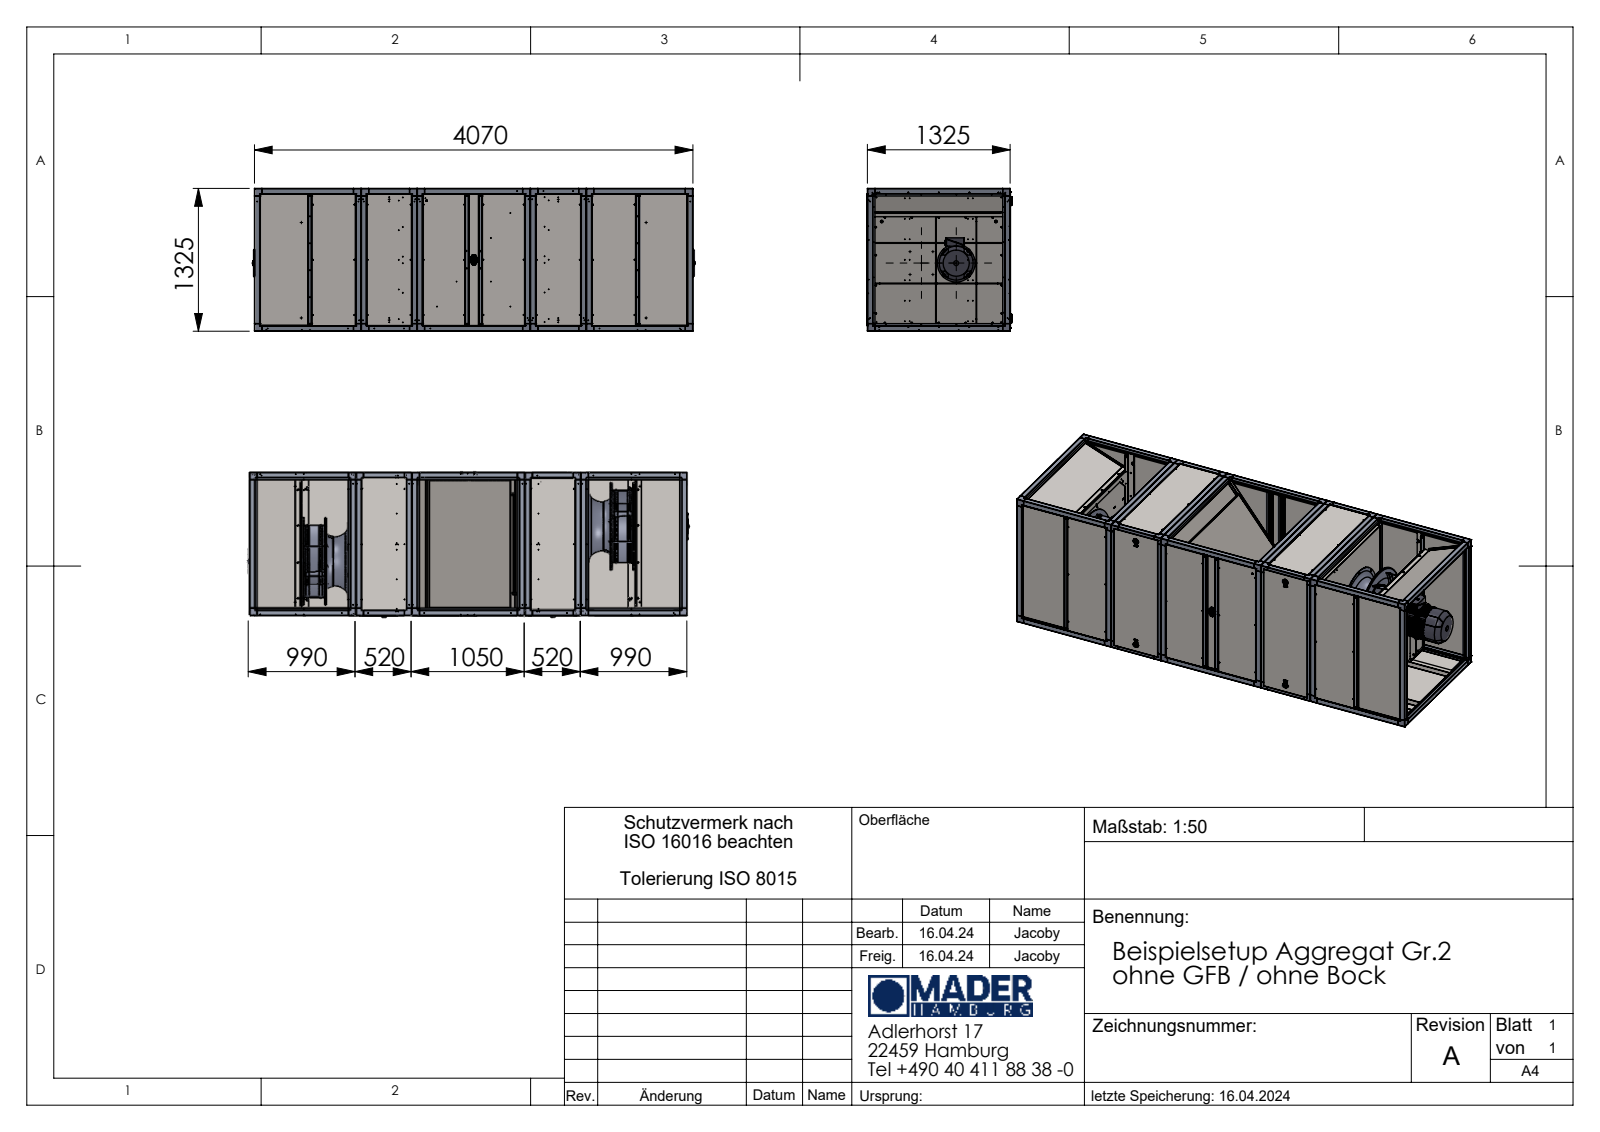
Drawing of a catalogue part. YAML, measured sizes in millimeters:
part_name: "Beispielsetup Aggregat Groesse 2 ohne GFB_ohne Bock"
step_written_by: "SolidWorks 2019 (CONFIG_CONTROL_DESIGN)"
units: millimeters
bodies: {solids: 341, faces: 24624, planar: 13058, cylindrical: 8482, other: 3084}
overall_size: [4108, 1344.73, 1325]
volume: 184600000
surface_area: 133200000
round_holes:
  - {diameter: 5, count: 200}
  - {diameter: 7, count: 82}
  - {diameter: 10, count: 65}
  - {diameter: 5.5, count: 34}
  - {diameter: 9, count: 34}
  - {diameter: 6, count: 33}
  - {diameter: 6.5, count: 32}
  - {diameter: 5.2, count: 28}
  - {diameter: 6.8, count: 19}
  - {diameter: 15, count: 16}
  - {diameter: 11, count: 14}
  - {diameter: 12, count: 14}
round_bosses_or_shafts:
  - {diameter: 4, count: 30}
  - {diameter: 50, count: 4}
  - {diameter: 46, count: 4}
  - {diameter: 16.25, count: 4}
  - {diameter: 4.5, count: 4}
  - {diameter: 810, count: 2}
  - {diameter: 710, count: 2}
  - {diameter: 350, count: 2}
partial_cylinders:
  - {radius: 2, count: 2614}
  - {radius: 1, count: 545}
  - {radius: 3, count: 161}
  - {radius: 0.75, count: 136}
  - {radius: 0.74, count: 94}
  - {radius: 1.8, count: 94}
  - {radius: 0.5, count: 88}
  - {radius: 2.8, count: 68}
face_to_face_distances: [1, 2, 23, 27, 24, 3, 1298, 25, 26, 1295]
hole_center_spacings: [1233, 1237.46, 511.5, 512, 105, 389.5, 250, 104.99]
